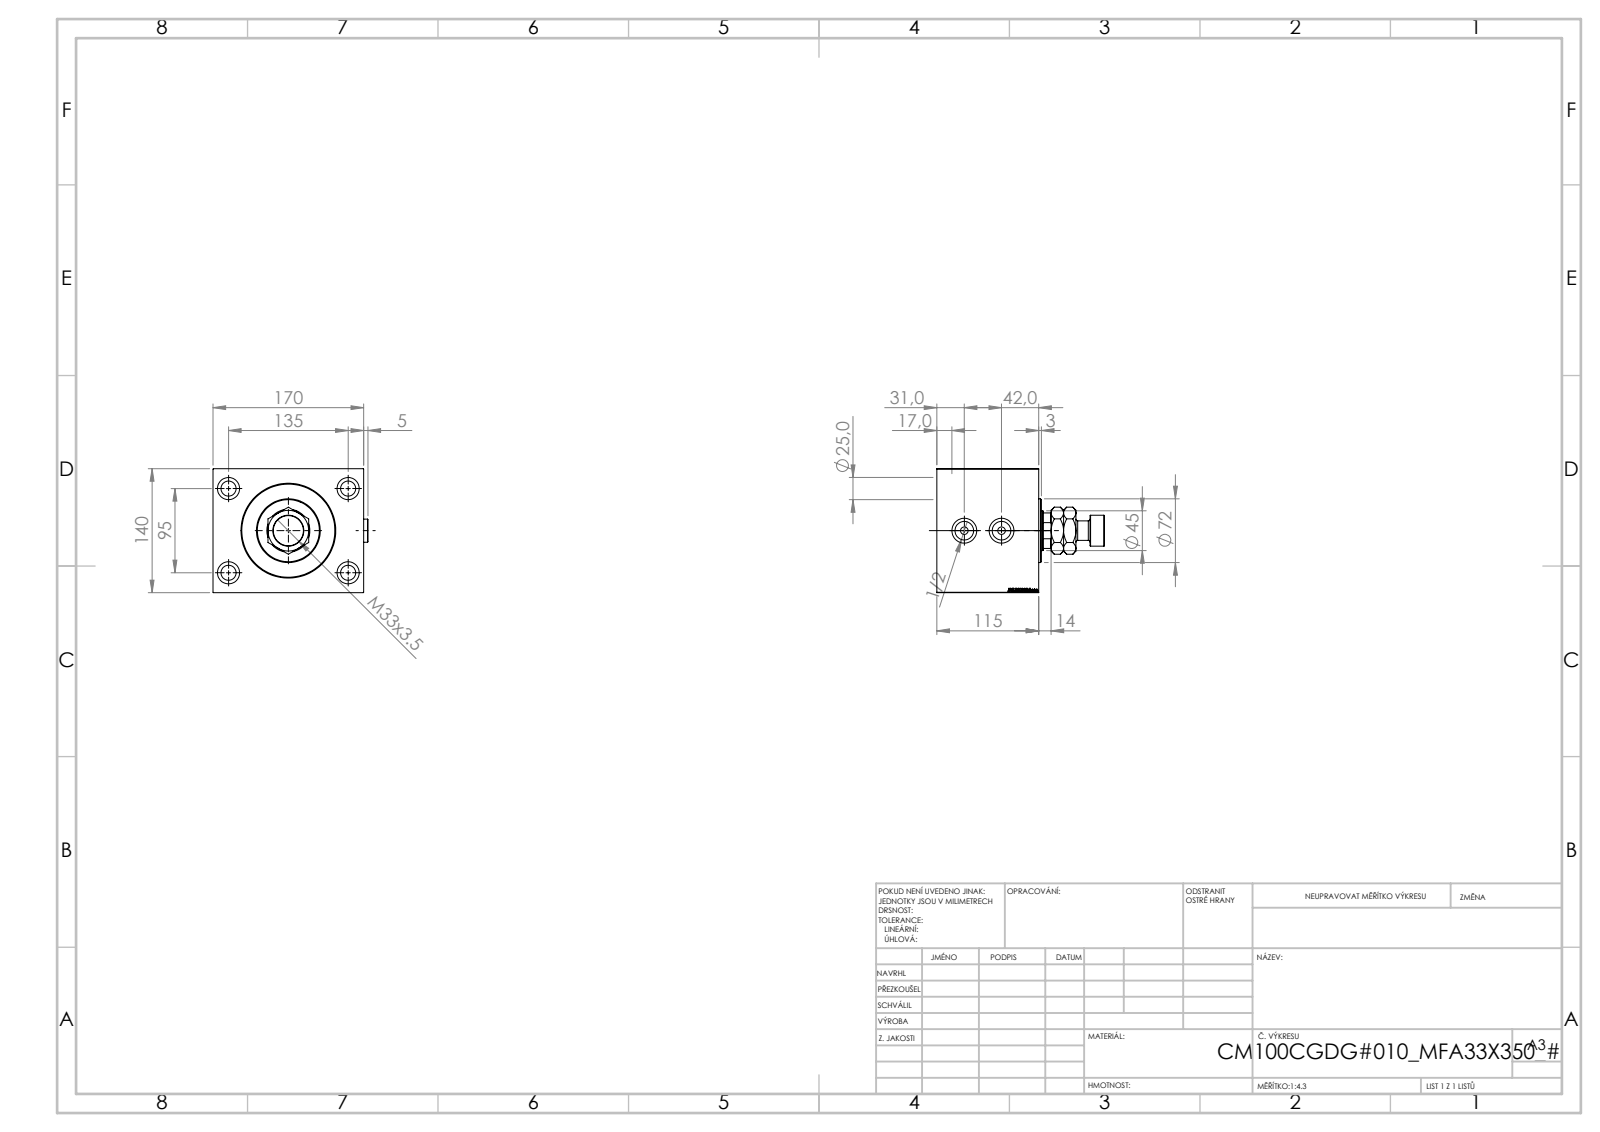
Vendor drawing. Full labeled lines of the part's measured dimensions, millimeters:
Part name (STEP PRODUCT): V450CM_VC_B; V450CM_C_VCP; Zatka_OIL_PORT; V450CM_C_Body (+1 more)
STEP written by: SolidWorks 2019 (CONFIG_CONTROL_DESIGN)
Units: millimetres
Bodies: 6 solids, 969 faces (459 planar, 80 cylindrical, 430 other)
Overall size (bounding box): 189 × 174.9 × 140
Volume: 2 578 000 mm³ · Surface area: 241 277 mm²
Round holes (diameter × count): ⌀17 ×4, ⌀25 ×4, ⌀8.5 ×2, ⌀20.96 ×2, ⌀28 ×2, ⌀31.5 ×1, ⌀45 ×1, ⌀48.5 ×1, ⌀100 ×1, ⌀102 ×1, ⌀105 ×1
Round bosses / shafts (diameter × count): ⌀26 ×2, ⌀72 ×1, ⌀35 ×1, ⌀22 ×1
Partial cylindrical surfaces — rounded edges, fillets, slot ends (radius × count): R22 ×1
Main face-to-face distances: 140, 115, 51, 64, 170, 21.6, 29.4, 93.4, 10, 31.6
Hole centre spacings: 82.54, 95, 135, 165.08, 42
